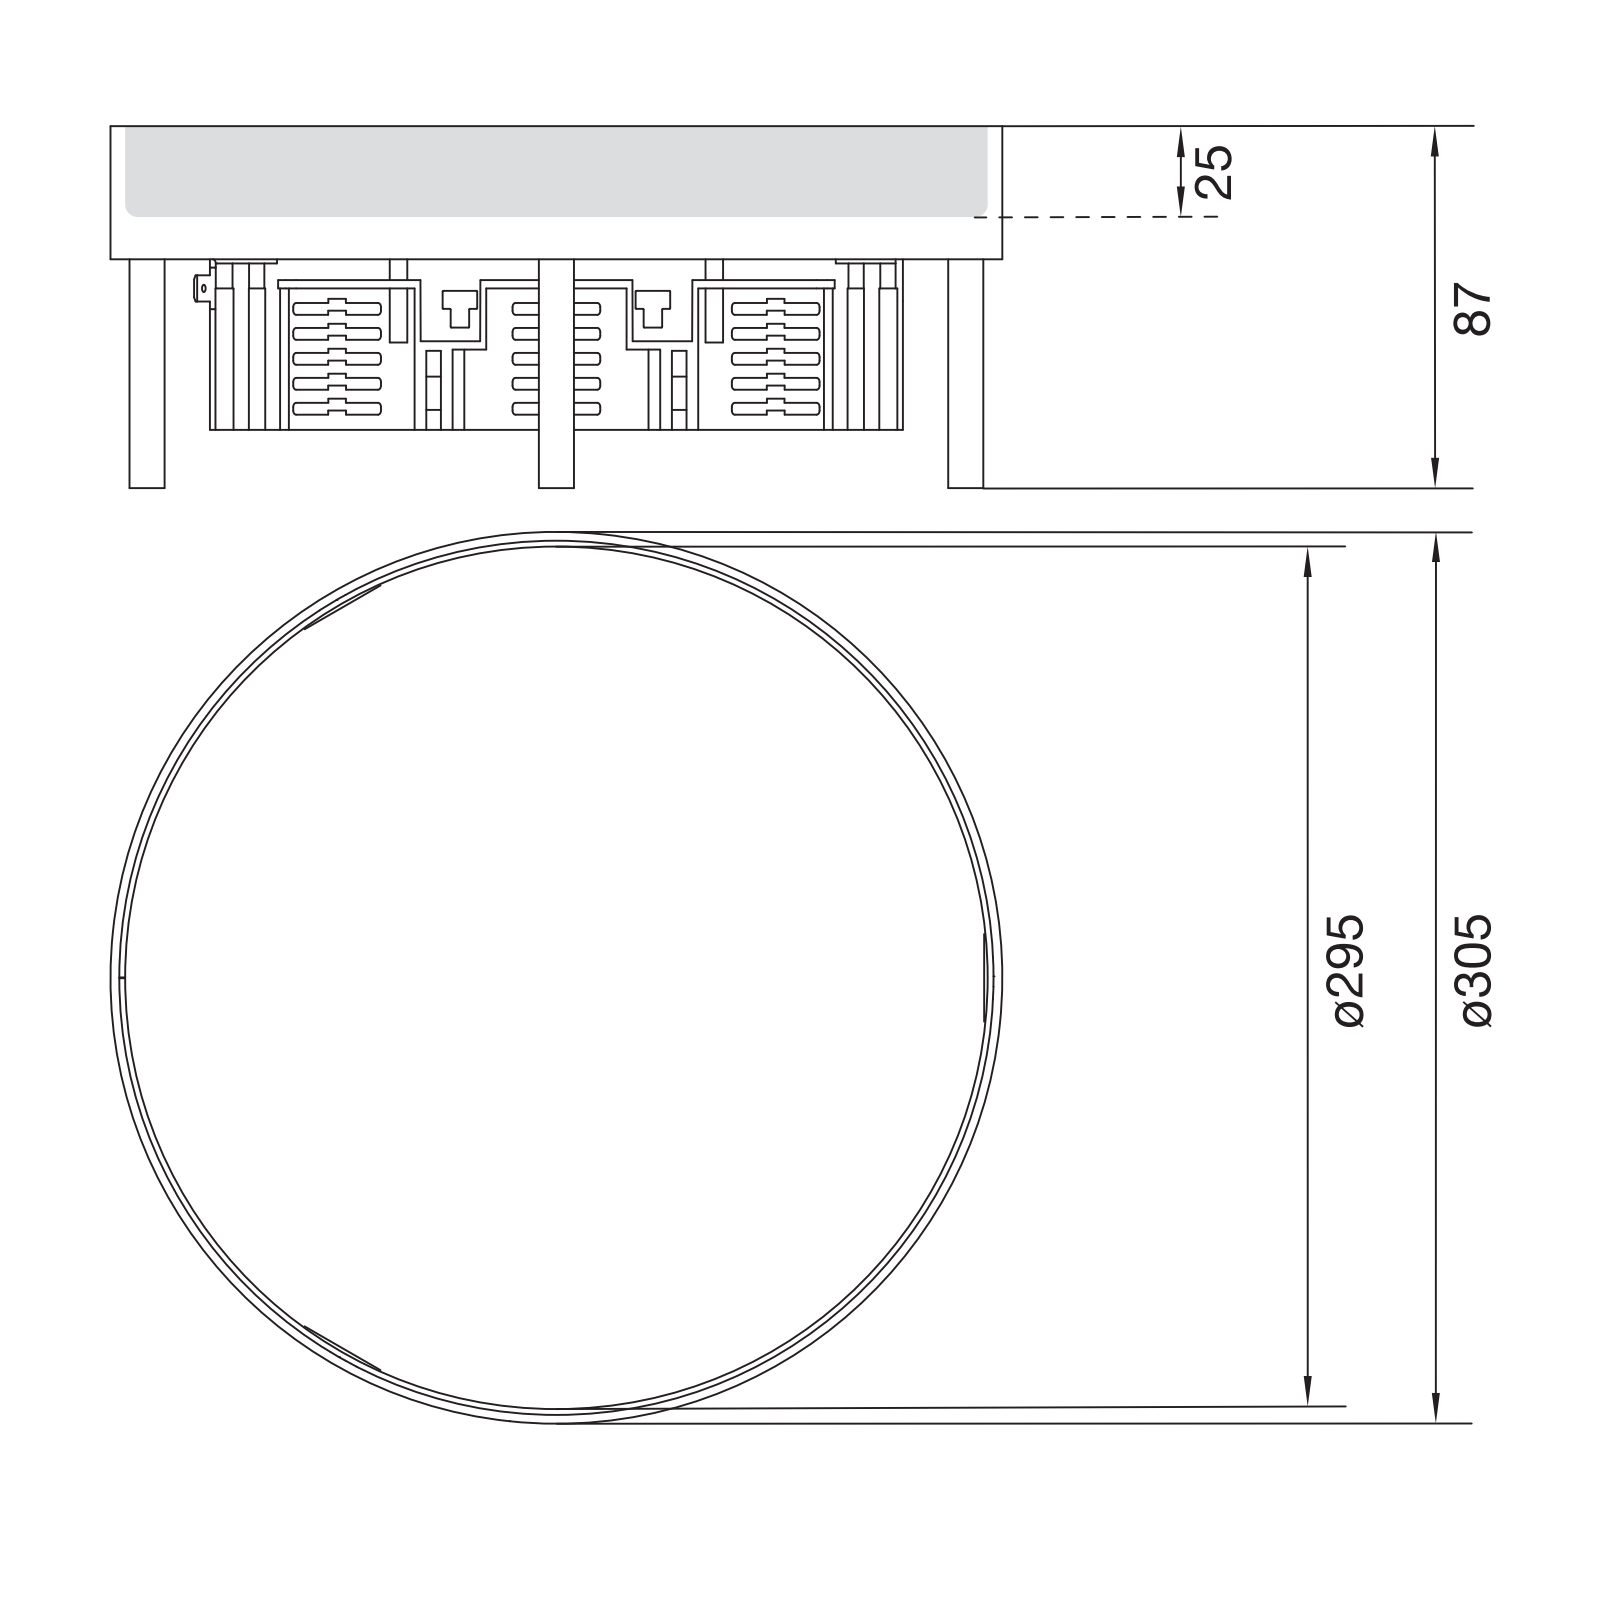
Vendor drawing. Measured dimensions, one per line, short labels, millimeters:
name: T-00736; T-00737; T-00738; T-00739 (+8 more)
written by: CREO PARAMETRIC BY PTC INC, 2022024 (AUTOMOTIVE_DESIGN)
unit: mm
bodies: 12 solids, 138 faces (66 planar, 72 cylindrical, 0 other)
size: 305 × 305 × 87
volume: 391 162 mm³; area: 392 772 mm²
holes: 6× ⌀3.8, 4× ⌀6.8, 4× ⌀8.5, 4× ⌀10.1
bosses: 4× ⌀12, 4× ⌀9.85, 1× ⌀305, 1× ⌀301, 1× ⌀299, 1× ⌀295
rounds: 8× R0.5, 1× R150
face distances: 2, 5, 2.5, 7, 3, 228.5, 229.5, 226, 227, 231
hole spacings: 59.51, 143.6, 197.99, 225.52, 260.65, 25.3, 108, 123.66
